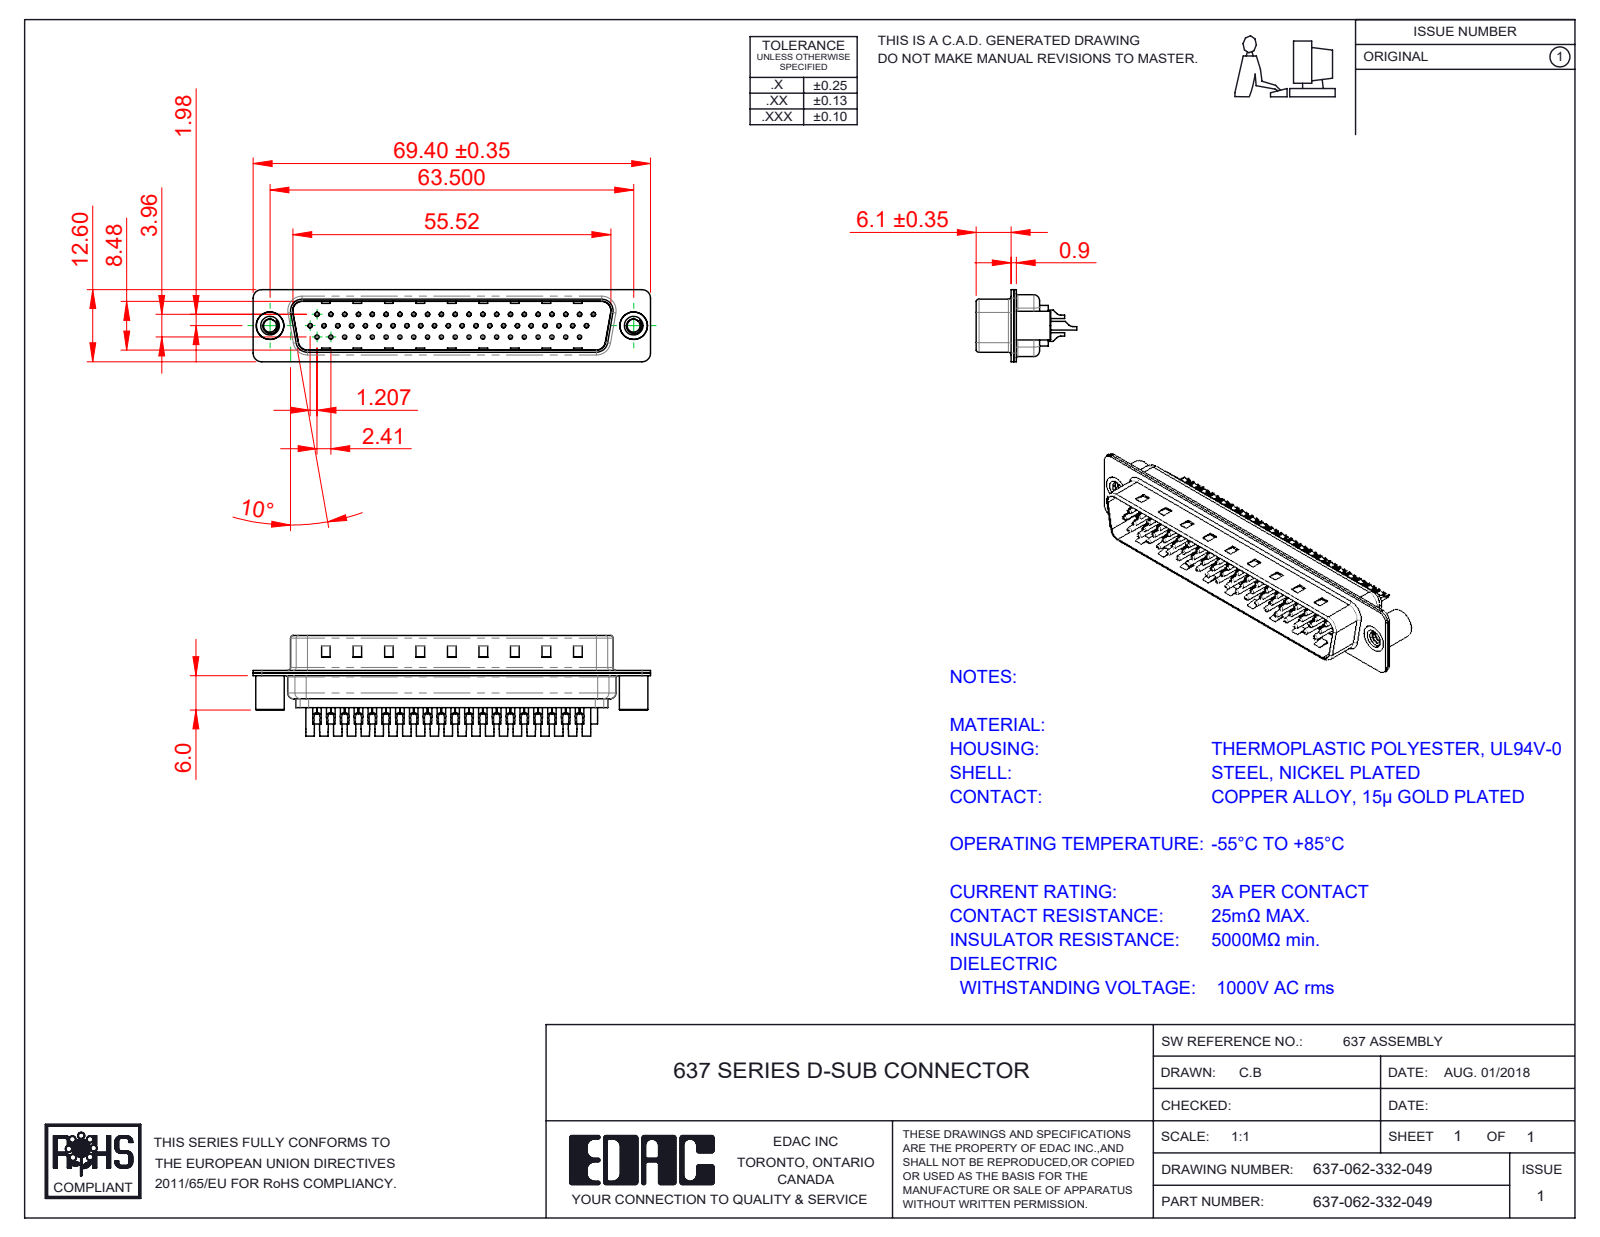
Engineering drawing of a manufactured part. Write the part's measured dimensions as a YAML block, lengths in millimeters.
part_name: "637 Housing_62 Contacts; 637 4-40 Threaded Standoff; 637 Contact Row 1_32; 637 Contact Row 3_32 (+4 more)"
step_written_by: "SolidWorks 2020 (CONFIG_CONTROL_DESIGN)"
units: millimeters
bodies: {solids: 67, faces: 4414, planar: 1073, cylindrical: 1967, other: 1374}
overall_size: [69.4, 17.55, 12.6]
volume: 3813
surface_area: 14366
round_holes:
  - {diameter: 0.35, count: 62}
  - {diameter: 1.1, count: 62}
  - {diameter: 1.6, count: 62}
  - {diameter: 2.26, count: 2}
  - {diameter: 4, count: 2}
  - {diameter: 4.8, count: 2}
round_bosses_or_shafts:
  - {diameter: 2, count: 62}
  - {diameter: 1.5, count: 62}
  - {diameter: 0.75, count: 62}
  - {diameter: 5, count: 2}
  - {diameter: 4.9, count: 2}
  - {diameter: 4.5, count: 2}
partial_cylinders:
  - {radius: 1.5, count: 16}
  - {radius: 2, count: 12}
  - {radius: 0.5, count: 8}
  - {radius: 1, count: 7}
  - {radius: 0.25, count: 4}
  - {radius: 0.55, count: 4}
  - {radius: 0.7, count: 4}
  - {radius: 0.95, count: 4}
face_to_face_distances: [0.45, 0.4, 0.7, 8.88, 8.48, 0.9, 9.64, 0.31, 0.76, 1.16]
hole_center_spacings: [7.24, 2.32, 2.41, 4.13, 9.65, 4.83, 14.48, 11.04]
